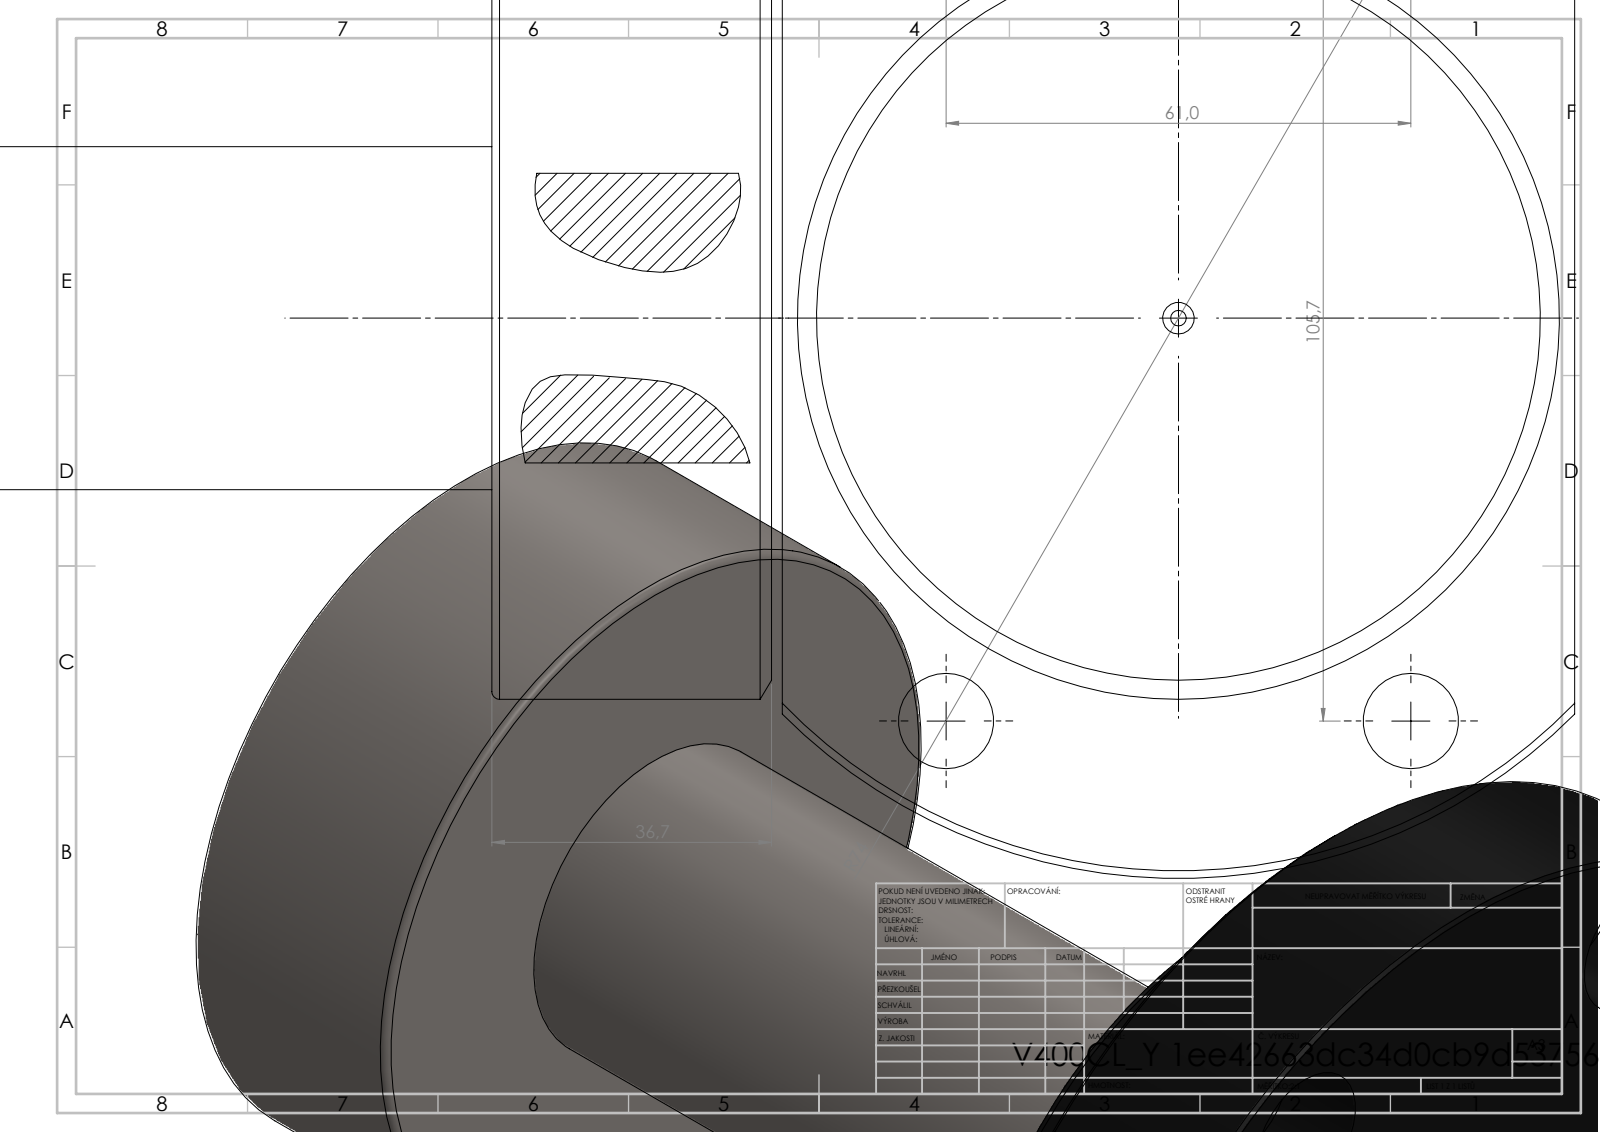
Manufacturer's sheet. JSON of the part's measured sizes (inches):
{"part_name": "V450CM_MALE_METRIC; V400CL_PC_Y; V400CL_VC_X", "step_written_by": "SolidWorks 2019 (CONFIG_CONTROL_DESIGN)", "units": "inches", "bodies": {"solids": 3, "faces": 117, "planar": 30, "cylindrical": 51, "other": 36}, "overall_size": [9.606, 5.787, 4.094], "volume_in3": 60.65, "surface_area_in2": 168.6, "round_holes": [[0.492, 4], [0.728, 4], [0.081, 1], [0.197, 1], [0.236, 1], [1.772, 1], [1.949, 1]], "round_bosses_or_shafts": [[3.937, 1], [3.898, 1], [1.299, 1], [1.22, 1]], "partial_cylinders_radius": [[0.876, 1], [2.894, 1]], "face_to_face_distances": [7.4, 1.445, 5.955, 5.648, 4.203, 1.752, 6.376, 4.931, 0.728, 1.024], "hole_center_spacings": [2.402, 2.402, 4.161, 4.805]}
